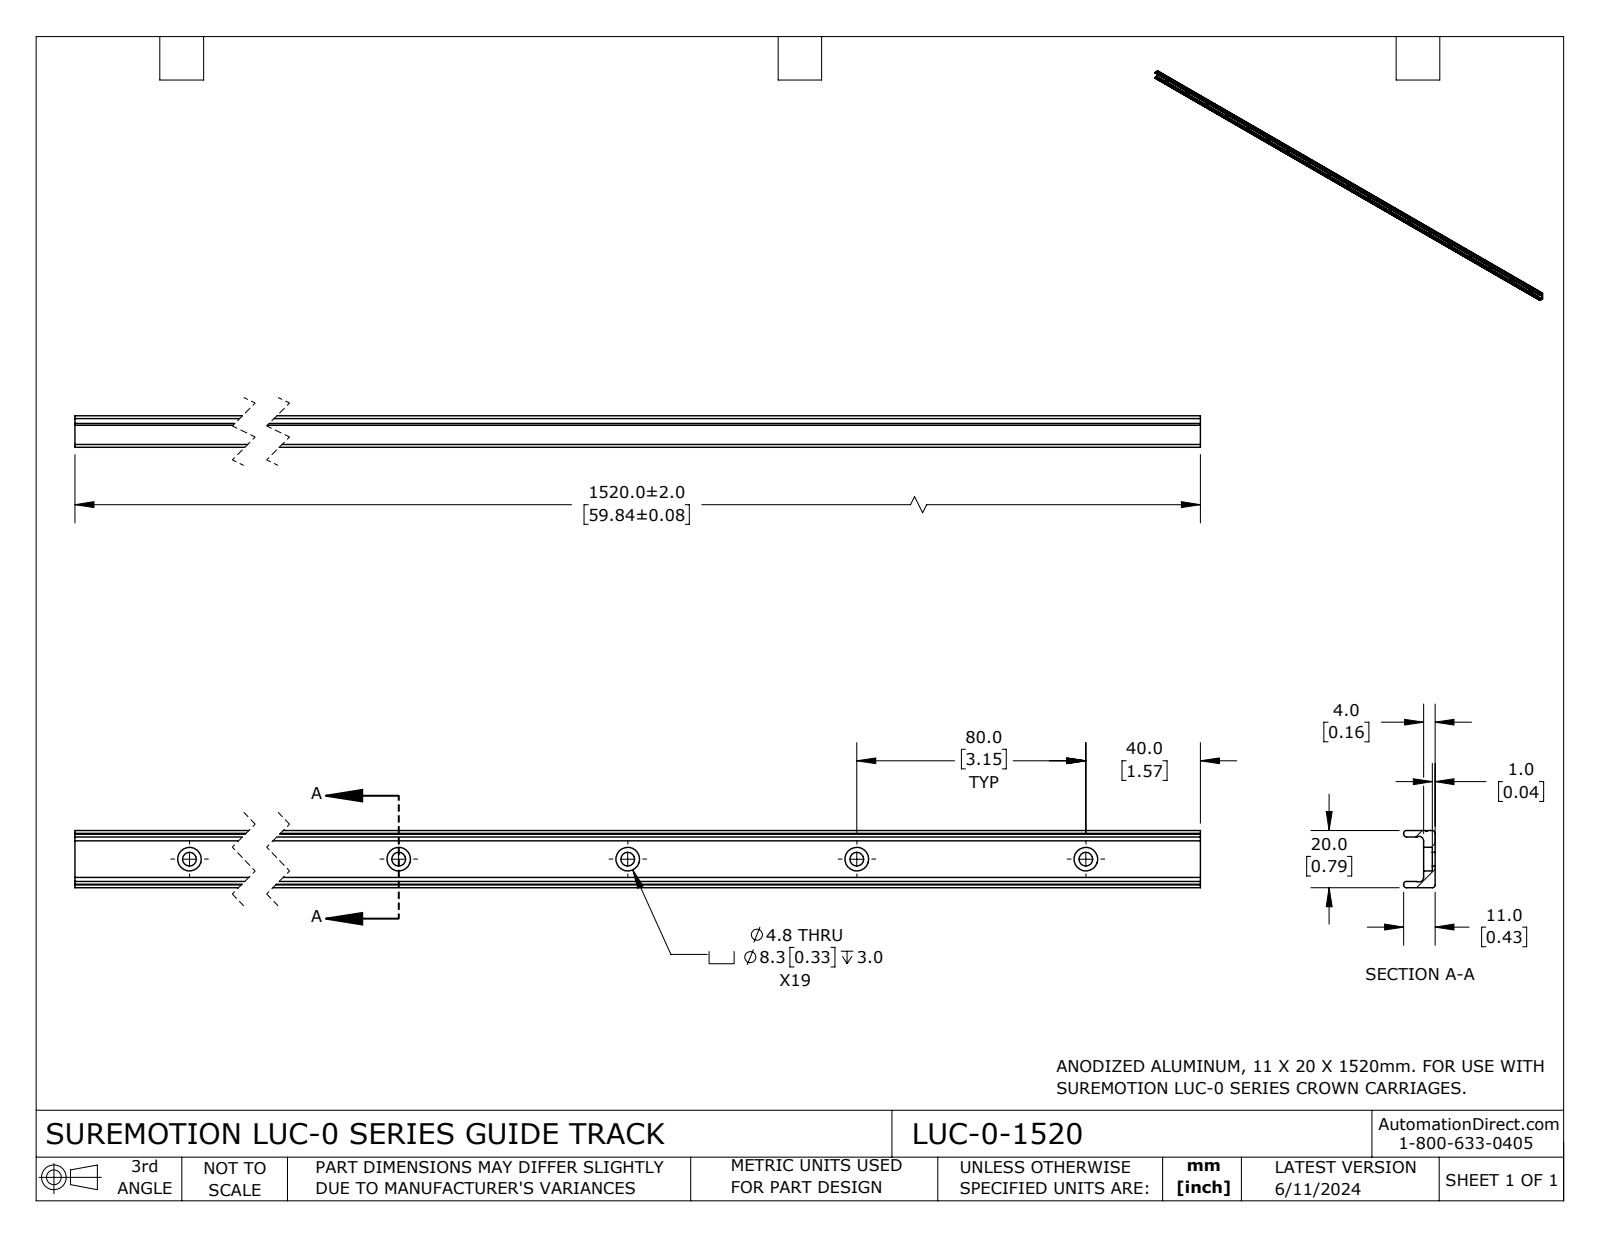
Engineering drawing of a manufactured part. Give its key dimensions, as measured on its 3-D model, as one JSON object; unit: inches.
{"part_name": "LUC-0-1520", "step_written_by": "SolidWorks 2023 (CONFIG_CONTROL_DESIGN)", "units": "inches", "bodies": {"solids": 1, "faces": 117, "planar": 30, "cylindrical": 87, "other": 0}, "overall_size": [59.843, 0.787, 0.433], "volume_in3": 10, "surface_area_in2": 173.7, "round_holes": [[0.189, 19], [0.325, 12], [0.325, 7]], "partial_cylinders_radius": [[0.039, 8], [0.063, 2], [0.013, 1]], "face_to_face_distances": [0.158, 0.787, 0.088, 0.7, 0.612, 0.433, 0.275, 0.04, 0.118, 0.393], "hole_center_spacings": [3.15, 6.299, 9.449, 12.598, 15.748, 18.898, 22.047, 25.197]}
